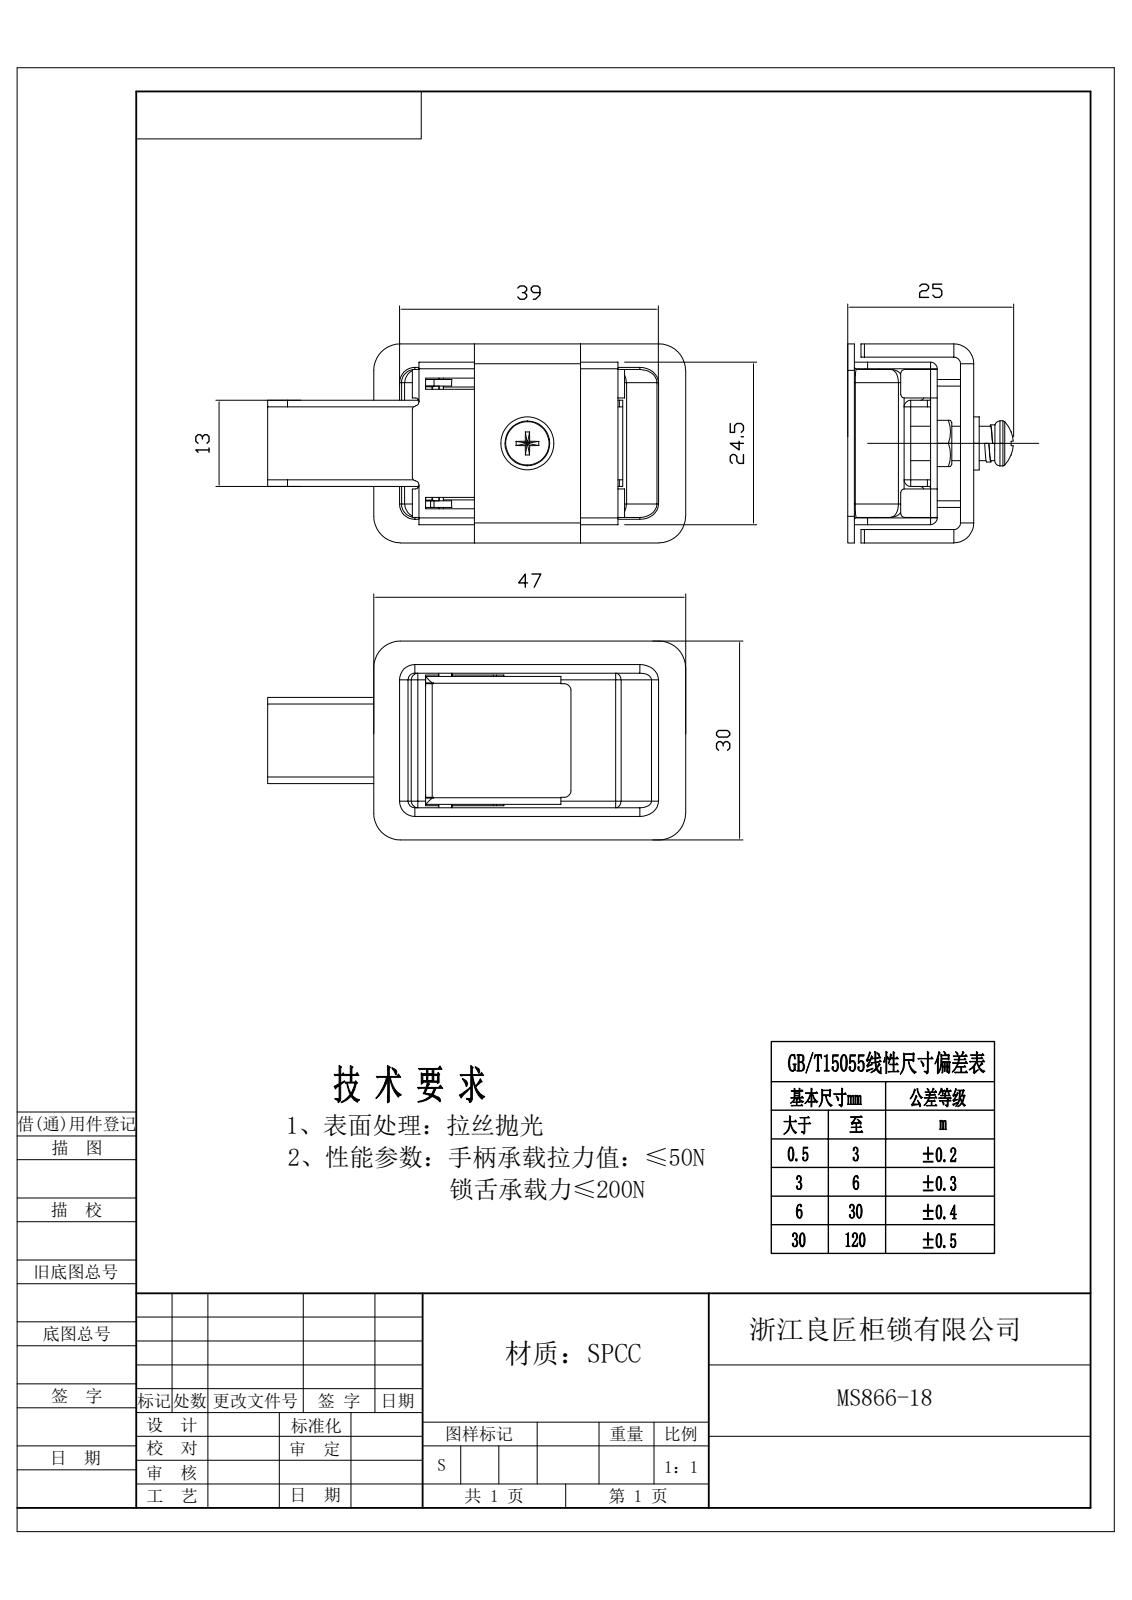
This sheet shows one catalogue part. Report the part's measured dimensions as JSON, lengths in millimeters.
{"step_written_by": "Rhino 8.5 (CONFIG_CONTROL_DESIGN)", "units": "millimeters", "bodies": {"solids": 0, "faces": 418, "planar": 242, "cylindrical": 133, "other": 43}, "overall_size": [63, 30, 24.93], "round_holes": [[3, 2], [1.6, 1], [2.1, 1]], "round_bosses_or_shafts": [[8, 1], [6.8, 1], [5.2, 1], [3, 1], [2, 1]], "partial_cylinders_radius": [[0.5, 19], [1, 18], [2, 11], [0.3, 4], [1.3, 4], [1.5, 4], [4, 4], [1, 3]], "face_to_face_distances": [1, 7.5, 8.5, 9.5, 2, 12.5, 6.5, 4, 11.5, 5], "hole_center_spacings": [6.14, 9, 15.06]}
